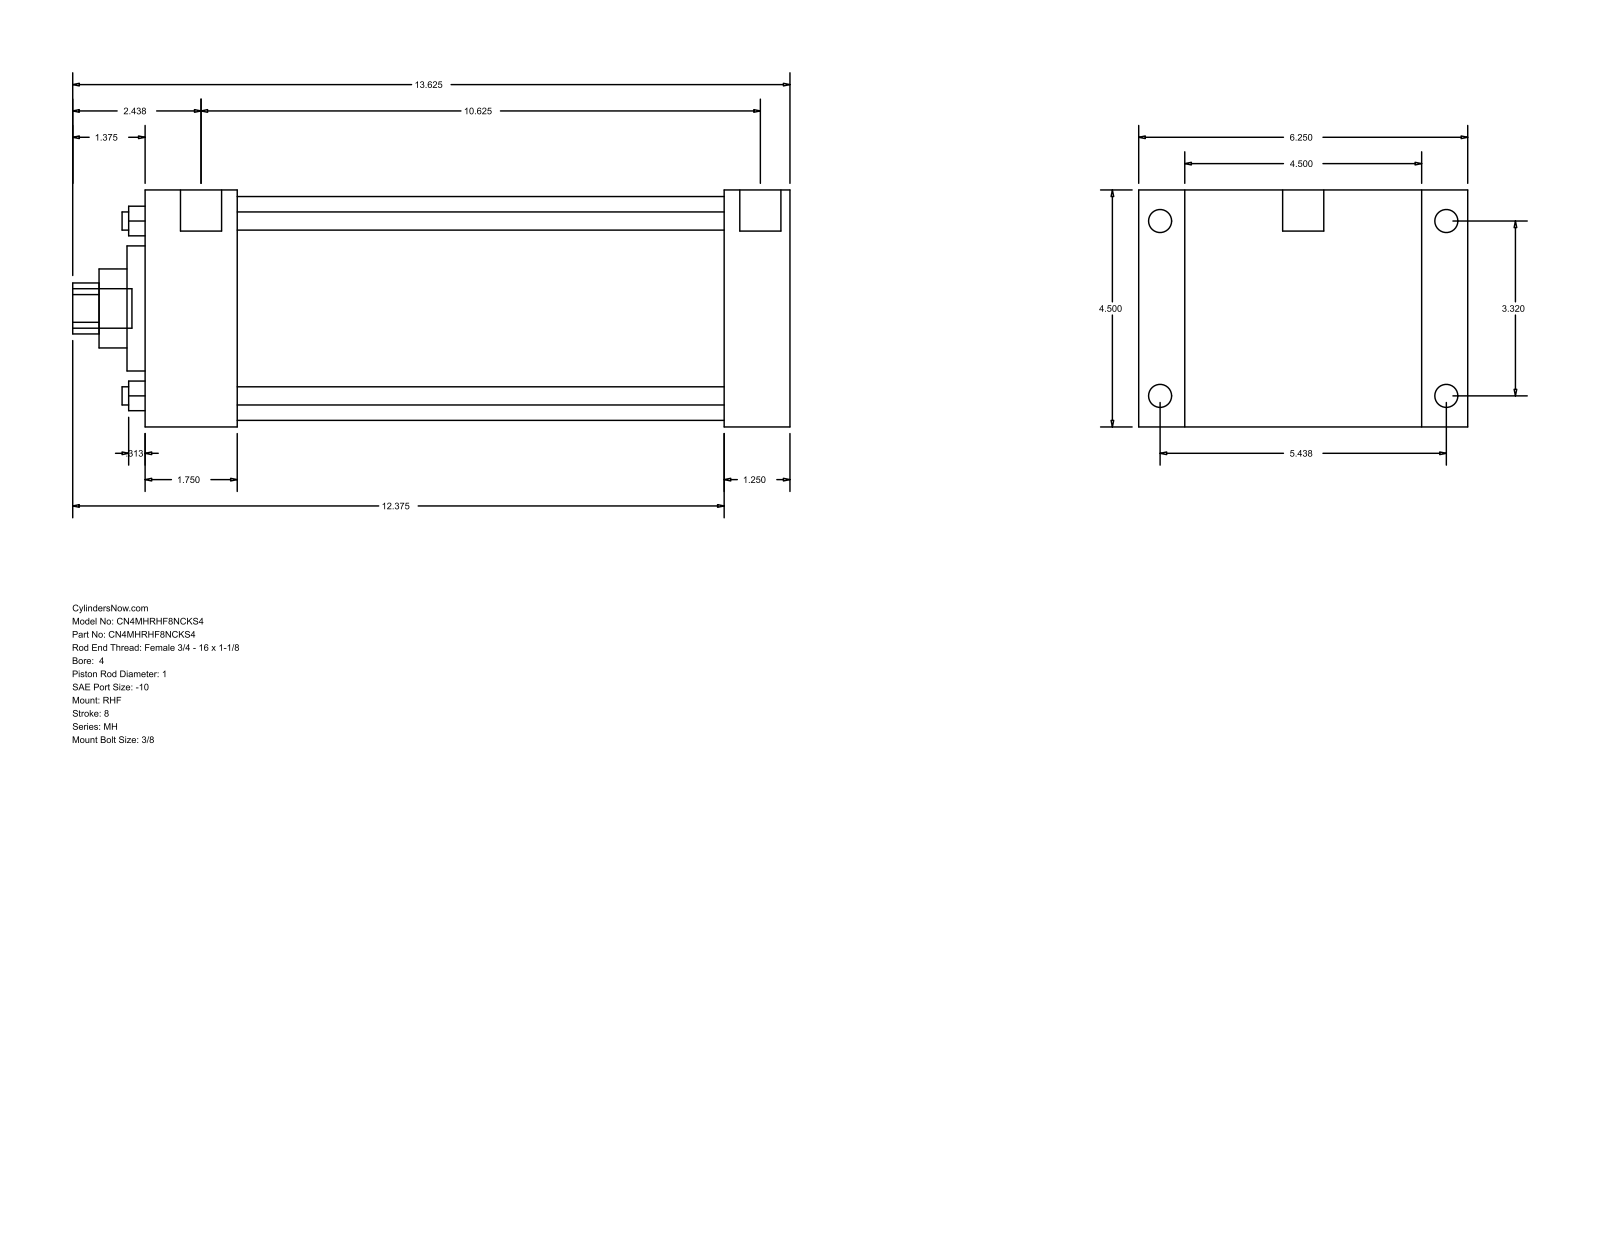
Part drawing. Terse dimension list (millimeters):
name: MH_RHF__0400_1
written by: GSSL Pune (CONFIG_CONTROL_DESIGN)
unit: mm
bodies: 0 solids, 90 faces (61 planar, 29 cylindrical, 0 other)
size: 346.07 × 158.75 × 114.3
holes: 4× ⌀8.76, 1× ⌀25.4, 1× ⌀38.1, 1× ⌀60.33, 1× ⌀107.95
bosses: 4× ⌀11.13, 4× ⌀8.73, 2× ⌀19.84, 1× ⌀19.05
rounds: 1× R12.29
face distances: 114.3, 311.15, 279.4, 31.75, 22.23, 136.53, 44.46, 234.94, 266.69, 158.76
hole spacings: 59.62, 84.32, 119.25
